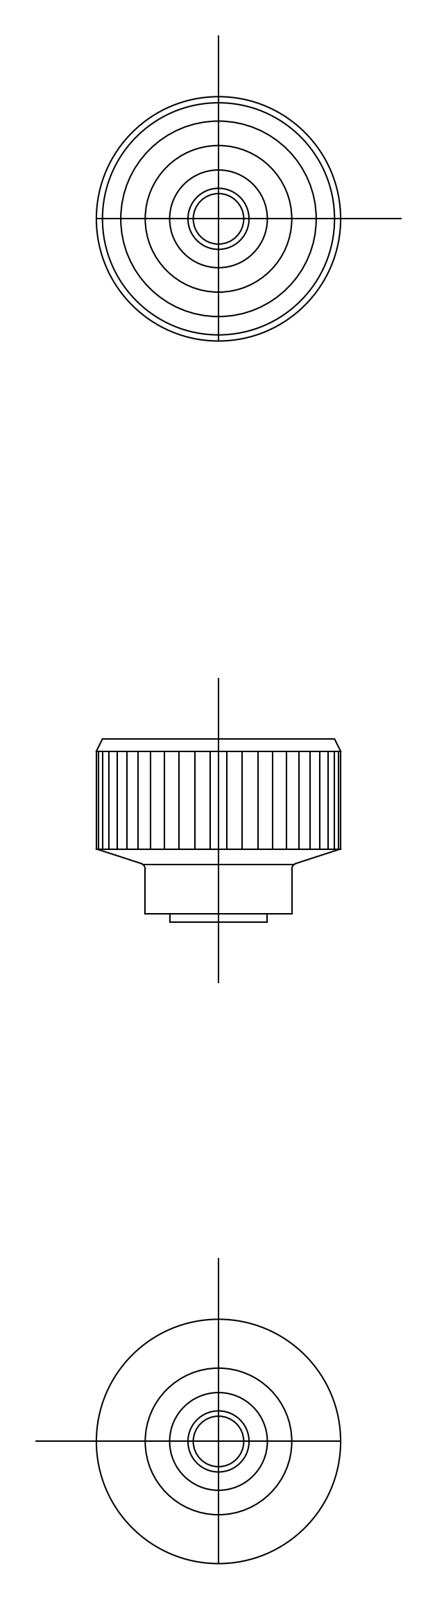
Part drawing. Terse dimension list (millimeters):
name: screw; knob; KKF_20_M5_4440_36
written by: CADfix (AUTOMOTIVE_DESIGN)
unit: mm
bodies: 2 solids, 31 faces (0 planar, 0 cylindrical, 31 other)
size: 20 × 20 × 15
volume: 2 550 mm³; area: 2 017 mm²
